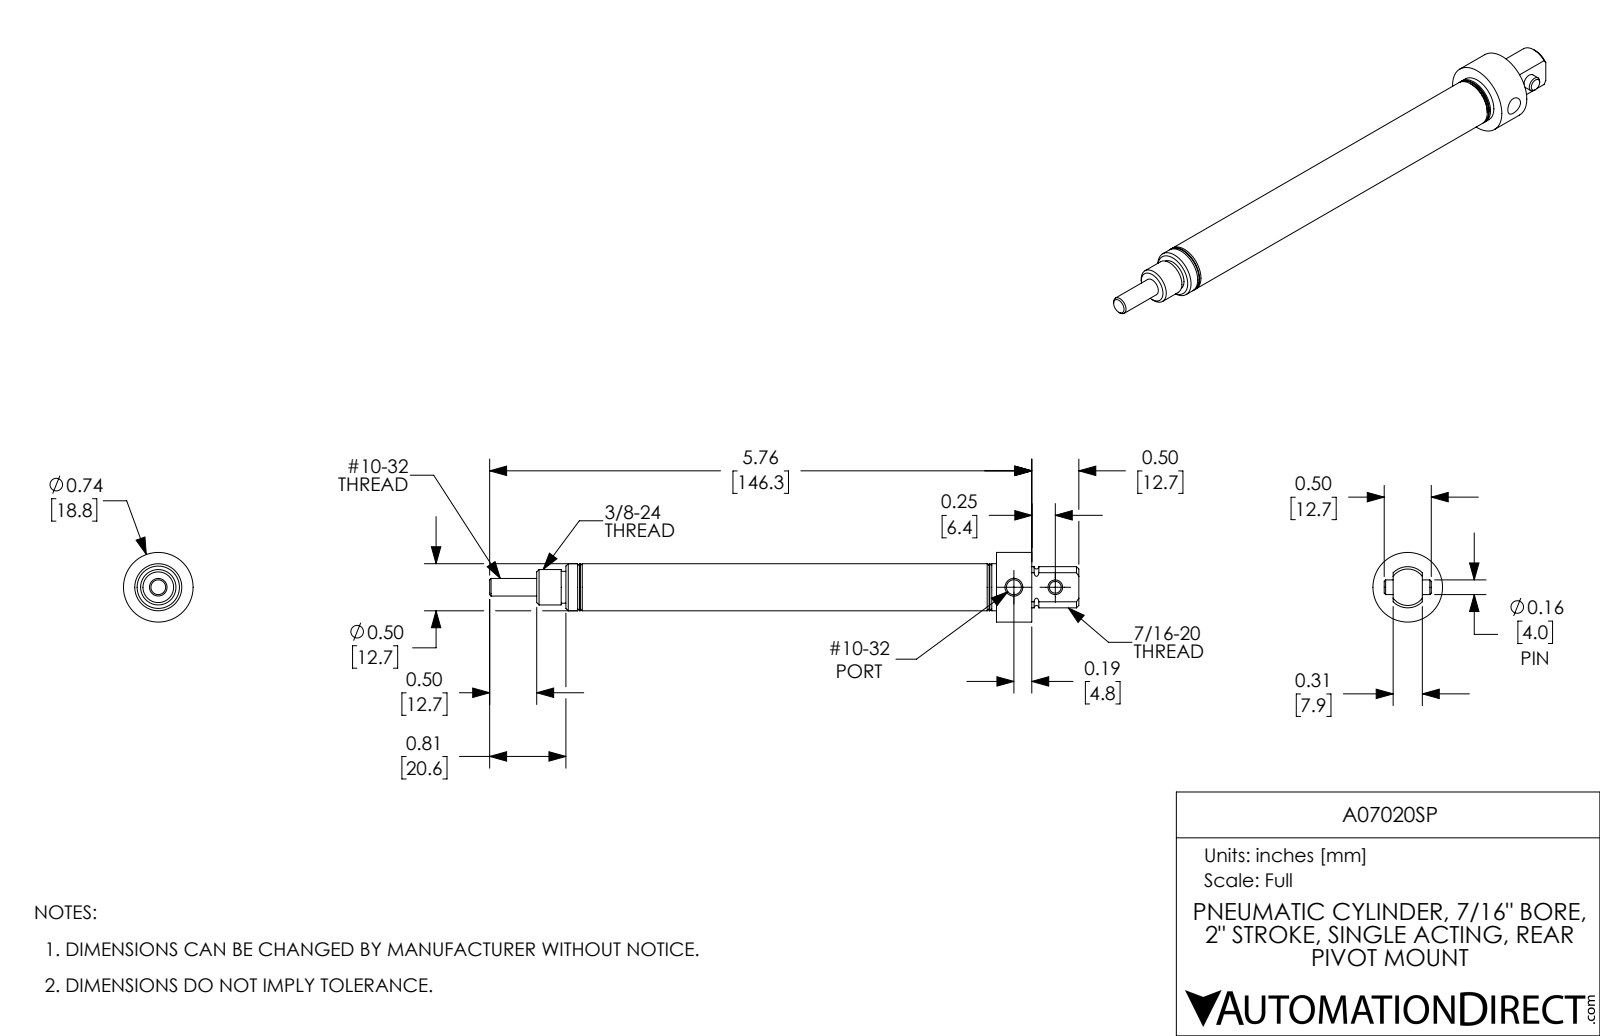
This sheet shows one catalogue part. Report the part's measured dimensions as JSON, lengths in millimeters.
{"part_name": "A07020SP-Pin; A07020SP-MainBody; A07020SP; A07020SP-Rod", "step_written_by": "SolidWorks 2017 (AUTOMOTIVE_DESIGN)", "units": "millimeters", "bodies": {"solids": 3, "faces": 82, "planar": 20, "cylindrical": 36, "other": 26}, "overall_size": [159, 18.8, 18.8], "volume_mm3": 14900, "surface_area_mm2": 12060, "round_holes": [[4, 1], [4, 1], [4.7, 1], [4.8, 1]], "round_bosses_or_shafts": [[18.8, 1], [12.7, 1], [11.1, 1], [9.6, 1], [8.6, 1]], "face_to_face_distances": [31.1, 12.7, 9.5, 21.6, 43.8, 7.9, 34.3, 94.6, 85.1, 63.5], "hole_center_spacings": [11.2]}
